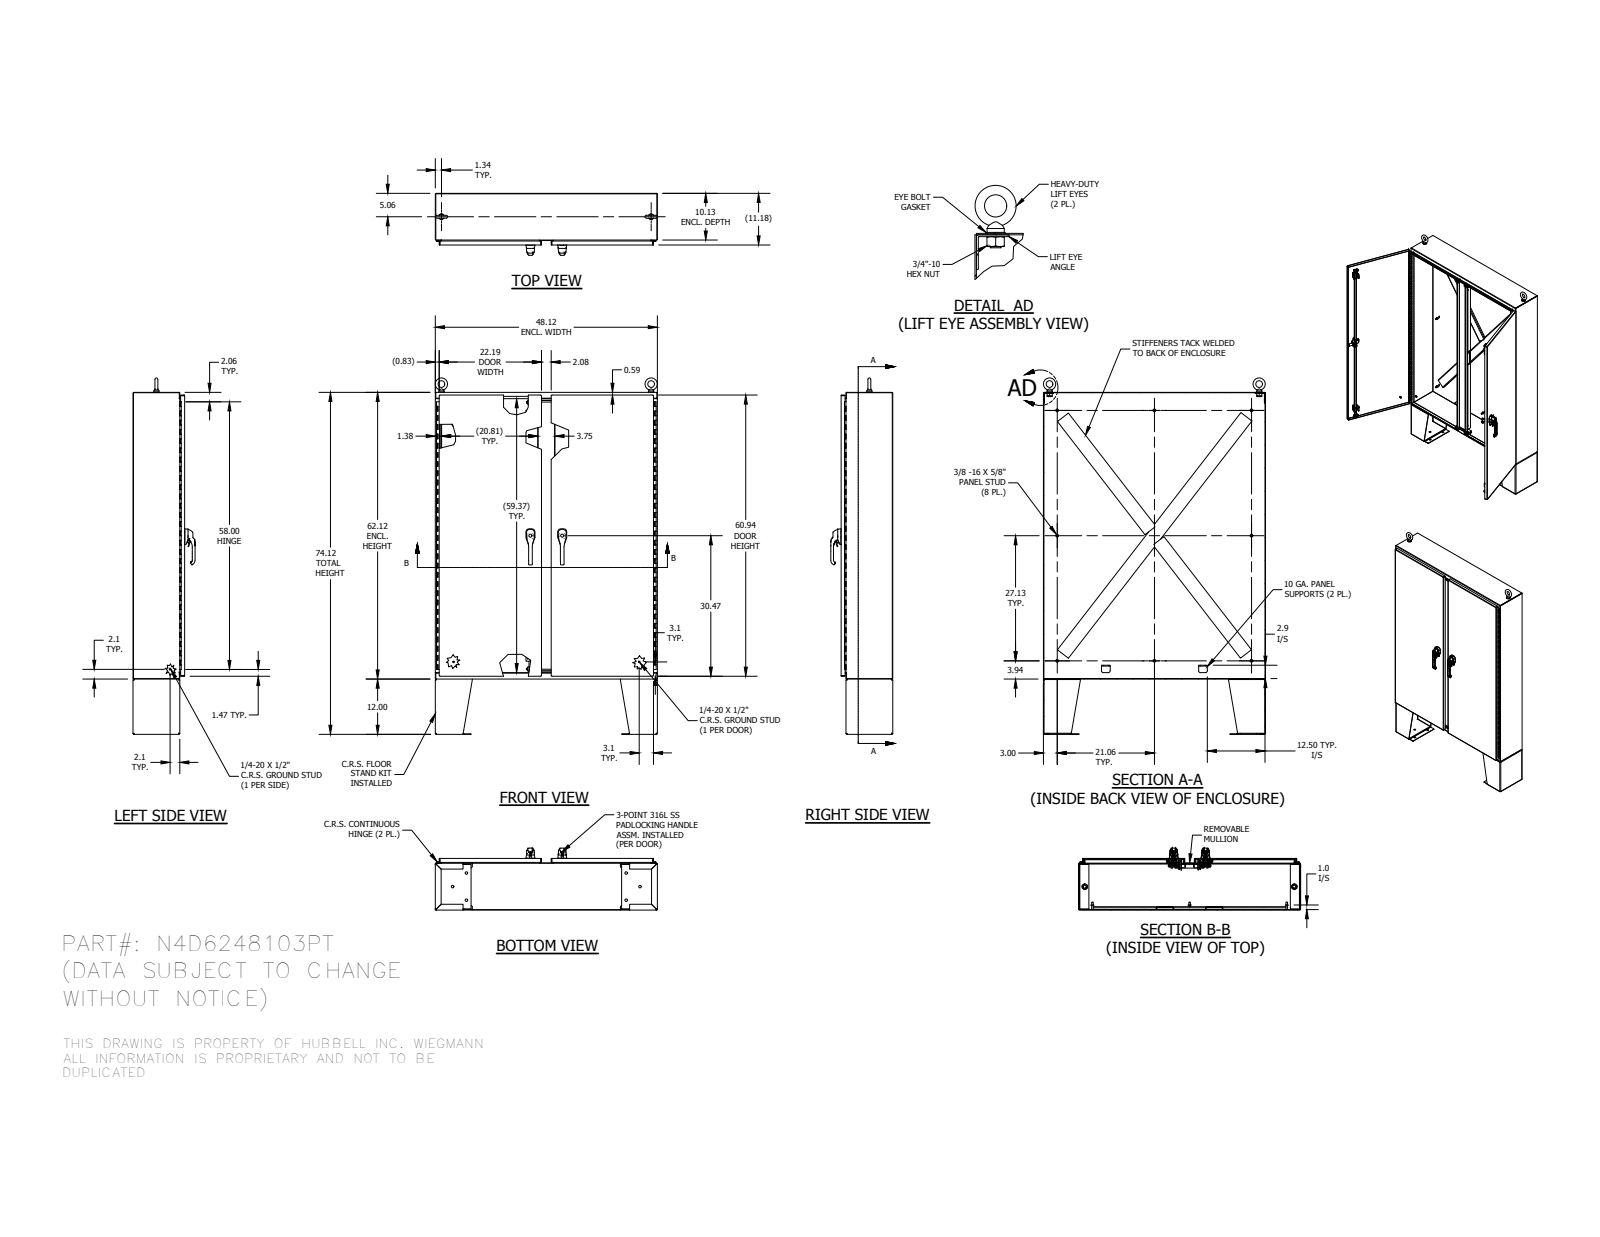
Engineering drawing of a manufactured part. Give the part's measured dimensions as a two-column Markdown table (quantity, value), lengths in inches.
| quantity | value |
| --- | --- |
| part name | N4D6248103PT; HFW3762_1; 3061_1; DIN3771_16X2_5_1 (+8 more) |
| STEP written by | SolidWorks 2014 (AUTOMOTIVE_DESIGN) |
| units | inches |
| bodies | 140 solids, 7612 faces (2862 planar, 3030 cylindrical, 1720 other) |
| overall size | 77.248 × 48.125 × 13.434 |
| volume | 1 111 in³ |
| surface area | 22 996 in² |
| round holes (diameter × count) | 0.563 × 18, 0.187 × 8, 0.262 × 8, 0.213 × 6, 0.281 × 6, 0.196 × 4, 0.241 × 4, 0.25 × 4, 0.252 × 4, 0.281 × 4, 0.315 × 4, 0.4 × 4 |
| round bosses / shafts (diameter × count) | 0.25 × 9, 0.625 × 8, 0.33 × 8, 0.236 × 6, 1 × 4, 0.563 × 4, 0.531 × 4, 0.5 × 4 |
| partial cylindrical surfaces (radius × count) | 0.02 × 343, 0.012 × 201, 0.019 × 44, 0.05 × 27, 0.079 × 27, 0.125 × 26, 0.094 × 25, 0.039 × 22 |
| main face-to-face distances | 0.094, 11.091, 10.998, 11.185, 10.031, 1.06, 48.031, 0.125, 62.031, 9.938 |
| hole center spacings | 6.894, 6.951, 28.888, 28.907, 0.886, 0.492, 0.76, 0.888 |
